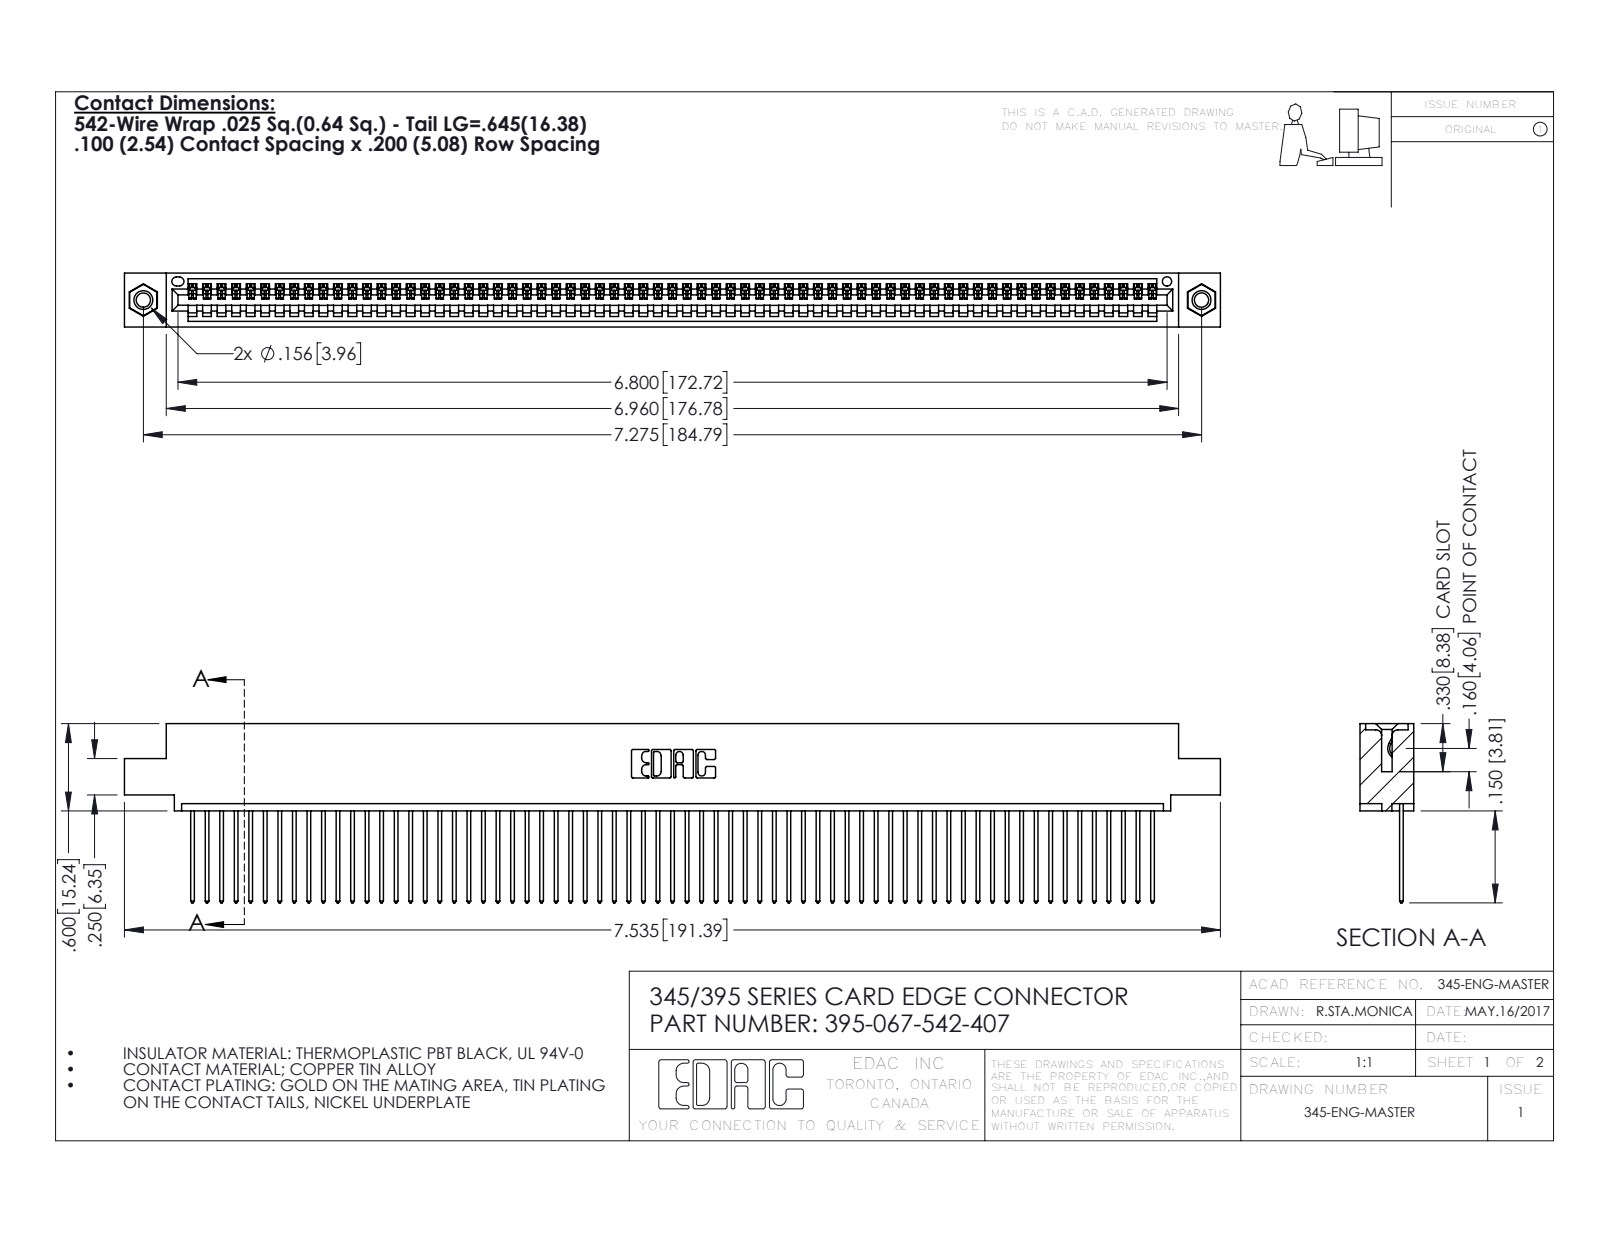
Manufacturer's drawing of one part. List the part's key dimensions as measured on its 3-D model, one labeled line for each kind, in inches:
Part name (STEP PRODUCT): 395-067-542-407; 345-250-001_345-250-005-103; 345 Part_0.110 Offset - 0.156 Dia-TI; 345-292-001_345-293-142
STEP written by: SolidWorks 2016 (CONFIG_CONTROL_DESIGN)
Units: inches
Bodies: 70 solids, 4076 faces (2796 planar, 1264 cylindrical, 16 other)
Overall size (bounding box): 7.535 × 1.232 × 0.37
Volume: 1.126 in³ · Surface area: 40.16 in²
Round holes (diameter × count): ⌀0.098 ×2, ⌀0.125 ×2, ⌀0.156 ×2, ⌀0.064 ×1
Round bosses / shafts (diameter × count): ⌀0.155 ×2
Partial cylindrical surfaces — rounded edges, fillets, slot ends (radius × count): R0.006 ×134, R0.01 ×134, R0.01 ×22, R0.007 ×6, R0.031 ×6, R0.026 ×3, R0.031 ×2, R0.04 ×2
Main face-to-face distances: 0.072, 0.298, 0.098, 0.272, 0.025, 0.37, 0.2, 0.225, 0.149, 0.072
Hole centre spacings: 0.27, 7.039, 7.275
